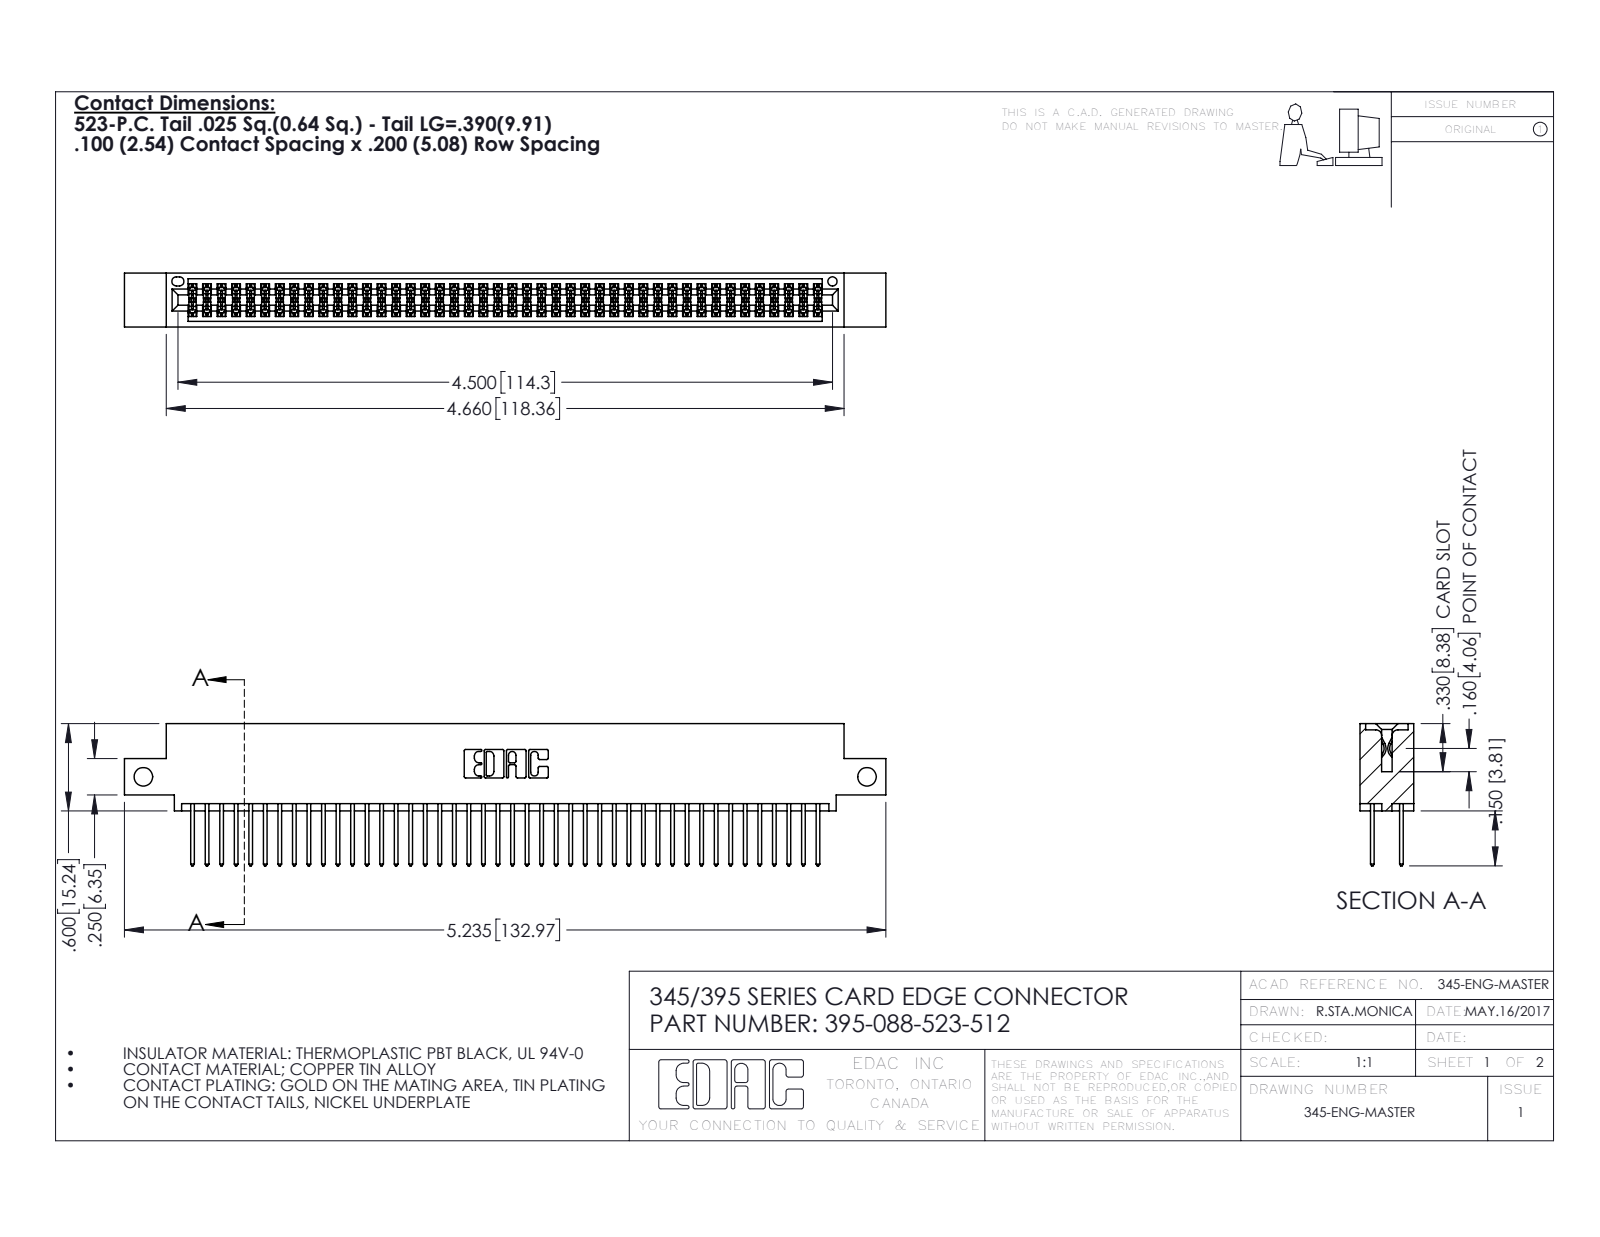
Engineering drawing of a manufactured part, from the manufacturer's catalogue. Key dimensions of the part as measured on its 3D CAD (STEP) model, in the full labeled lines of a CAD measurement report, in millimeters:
Part name (STEP PRODUCT): 395-088-523-512; 345 Part_0.110 Offset - Side Mount; 345-292-001_345-293-123
STEP written by: SolidWorks 2016 (CONFIG_CONTROL_DESIGN)
Units: millimetres
Bodies: 89 solids, 4530 faces (2988 planar, 1542 cylindrical, 0 other)
Overall size (bounding box): 133 × 24.8 × 9.4
Volume: 13 000 mm³ · Surface area: 19 950 mm²
Round holes (diameter × count): ⌀3.3 ×2, ⌀1.6 ×1
Partial cylindrical surfaces — rounded edges, fillets, slot ends (radius × count): R0.2 ×132, R0.3 ×88, R0.3 ×22, R0.2 ×6, R0.8 ×6, R0.7 ×3, R0.4 ×2, R0.5 ×2
Main face-to-face distances: 7.6, 1.8, 5.1, 2.5, 6.9, 0.6, 9.4, 5.7, 4.4, 3.8
Hole centre spacings: 126.4
